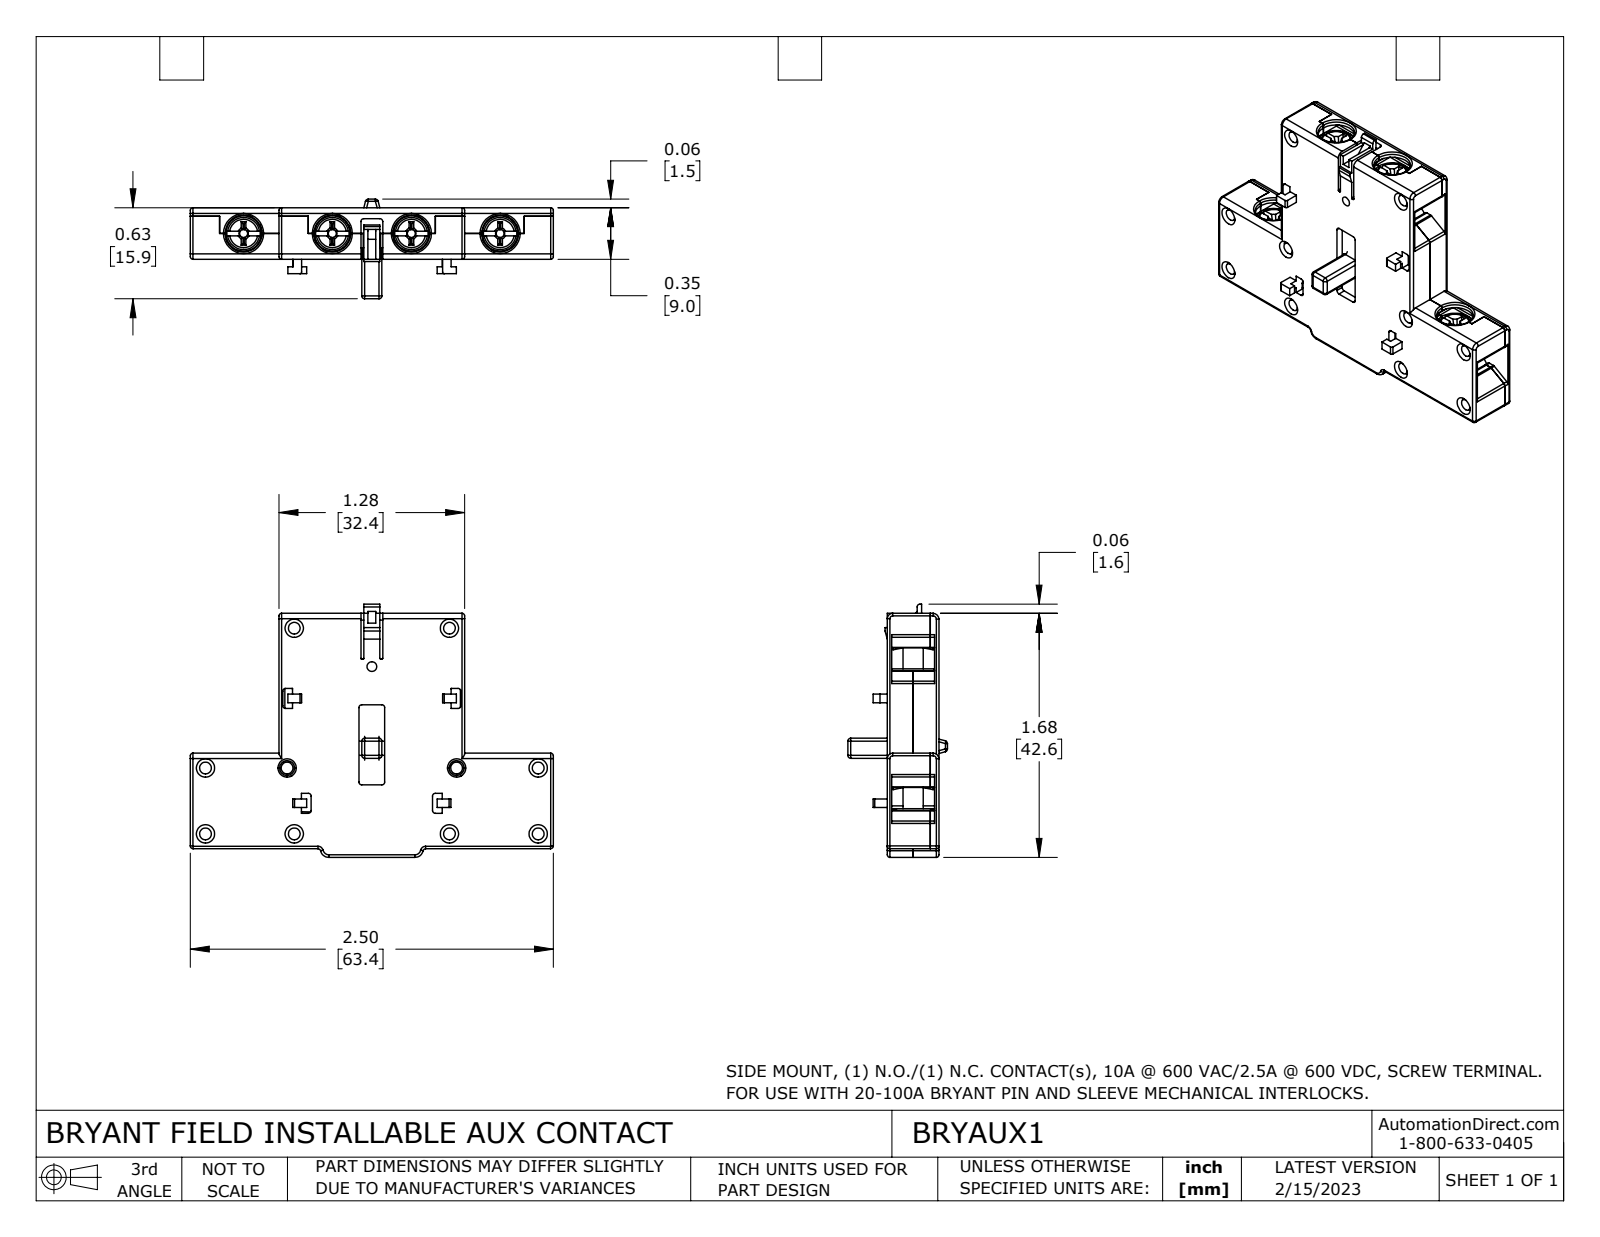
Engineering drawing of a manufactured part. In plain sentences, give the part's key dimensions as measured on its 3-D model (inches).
The part is named "BRYAUX1". Its 3-D file was written by "SolidWorks 2021 (CONFIG_CONTROL_DESIGN)". It is 11 solids with 1643 faces: 943 planar, 512 cylindrical and 188 other. Overall it measures 2.496 by 1.74 by 0.685 inches. Its volume is 0.836 cubic inches and its surface area 29.62 square inches. Round holes: 10 of diameter 0.126, 4 of diameter 0.11, 4 of diameter 0.252, 2 of diameter 0.094, 2 of diameter 0.118, 2 of diameter 0.177, 2 of diameter 0.217, 1 of diameter 0.067. Round bosses or shafts: 4 of diameter 0.138, 4 of diameter 0.098, 2 of diameter 0.165, 2 of diameter 0.157. Partial cylindrical surfaces (rounded edges, fillets, slot ends): 103 of radius 0.02, 52 of radius 0.012, 34 of radius 0.011, 18 of radius 0.018, 10 of radius 0.016, 9 of radius 0.039, 8 of radius 0.008, 8 of radius 0.047. The main face-to-face distances are 0.295, 0.059, 0.354, 0.03, 0.244, 0.236, 0.118, 0.177, 0.303, 0.325. The hole center spacings are 0.61, 0.235, 0.453, 0.456, 0.561, 0.595, 0.657, 0.678.
